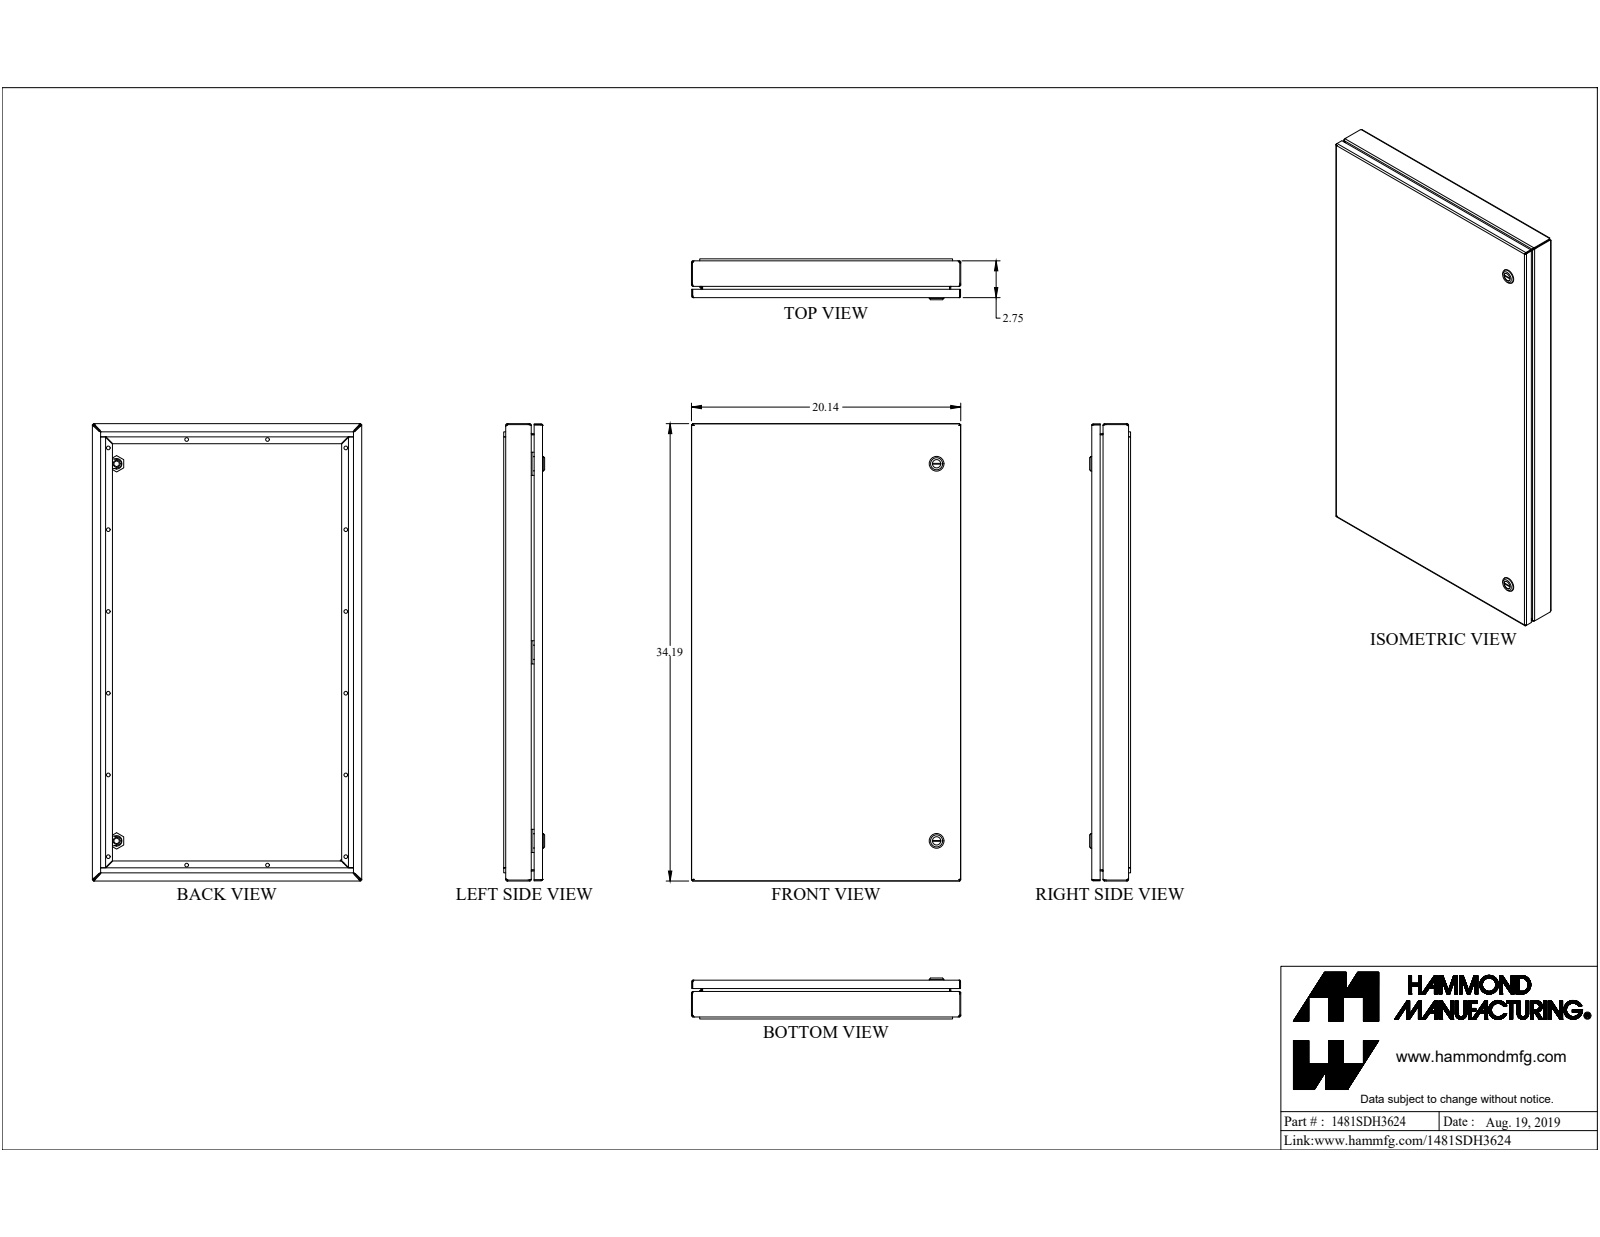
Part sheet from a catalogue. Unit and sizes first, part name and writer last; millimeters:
Units: millimetres
Overall size (bounding box): 868.4 × 511.6 × 77.7
Round holes (diameter × count): ⌀7.1 ×16, ⌀5.9 ×2, ⌀15.9 ×2, ⌀19.9 ×2, ⌀4.4 ×1, ⌀6.1 ×1, ⌀6.1 ×1
Round bosses / shafts (diameter × count): ⌀27.9 ×2, ⌀13.3 ×2, ⌀11.6 ×1, ⌀10.1 ×1, ⌀9 ×1, ⌀8 ×1, ⌀7.4 ×1, ⌀6.4 ×1
Partial cylindrical surfaces — rounded edges, fillets, slot ends (radius × count): R0.9 ×28, R2.7 ×28, R9.7 ×12, R482.7 ×8, R0.2 ×6, R1.6 ×6, R3.2 ×4, R6.4 ×4
Main face-to-face distances: 1.8, 65.5, 21.4, 44.1, 67.3, 509.7, 63.7, 68, 46.6, 2.5
Hole centre spacings: 547.6, 155.2, 310.4, 451.2, 465.6, 477.1, 648.3, 149.7
Volume: 1 817 000 mm³ · Surface area: 1 877 000 mm²
Bodies: 31 solids, 778 faces (449 planar, 215 cylindrical, 114 other)
Part name (STEP PRODUCT): 1481SDH3624
STEP written by: SolidWorks 2019 (CONFIG_CONTROL_DESIGN)
